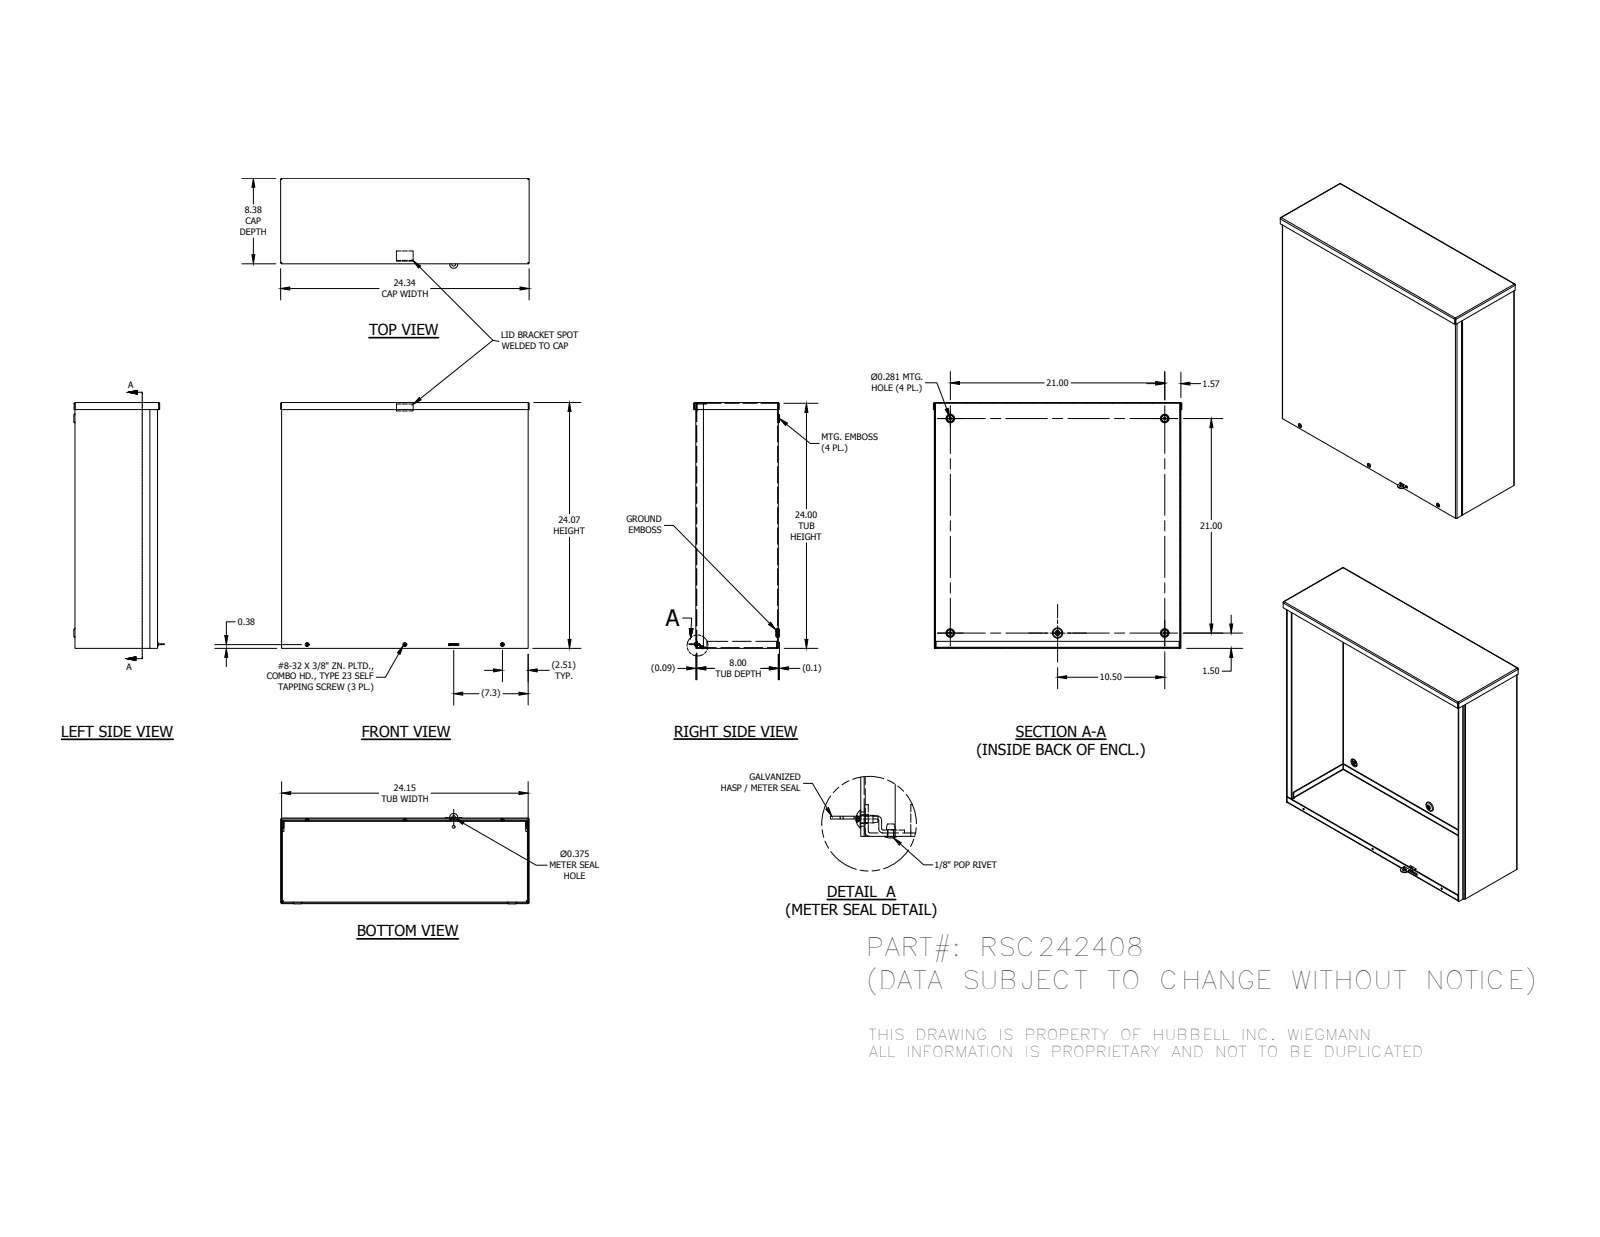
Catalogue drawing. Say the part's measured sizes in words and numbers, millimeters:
The part is named "RSC242408BKPA; RSC2408EWPA; RSC2424LFA; RSC2408CPA (+5 more)". Its 3-D file was written by "Autodesk Inventor 2014 (AUTOMOTIVE_DESIGN)". It is 10 solids with 350 faces: 193 planar, 66 cylindrical and 91 other. Overall it measures 618.12 by 612.5 by 224.8 millimeters. Its volume is 2 477 000 cubic millimeters and its surface area 2 655 000 square millimeters. Round holes: 6 of diameter 7.94, 4 of diameter 7.14, 3 of diameter 3.73, 1 of diameter 3.17, 1 of diameter 3.45, 1 of diameter 4.34, 1 of diameter 9.52. Round bosses or shafts: 3 of diameter 9.75, 3 of diameter 4.17, 1 of diameter 6.65, 1 of diameter 5.93, 1 of diameter 3.17. Partial cylindrical surfaces (rounded edges, fillets, slot ends): 19 of radius 0.79, 17 of radius 2.67, 2 of radius 2.37, 1 of radius 10.16. The main face-to-face distances are 1.88, 203.6, 205.48, 201.72, 609.6, 611.48, 607.72, 613.36, 607.54, 3.94. The hole center spacings are 242.89, 268.23, 510.39, 533.4, 622.05, 638.55, 37.2, 485.78.
